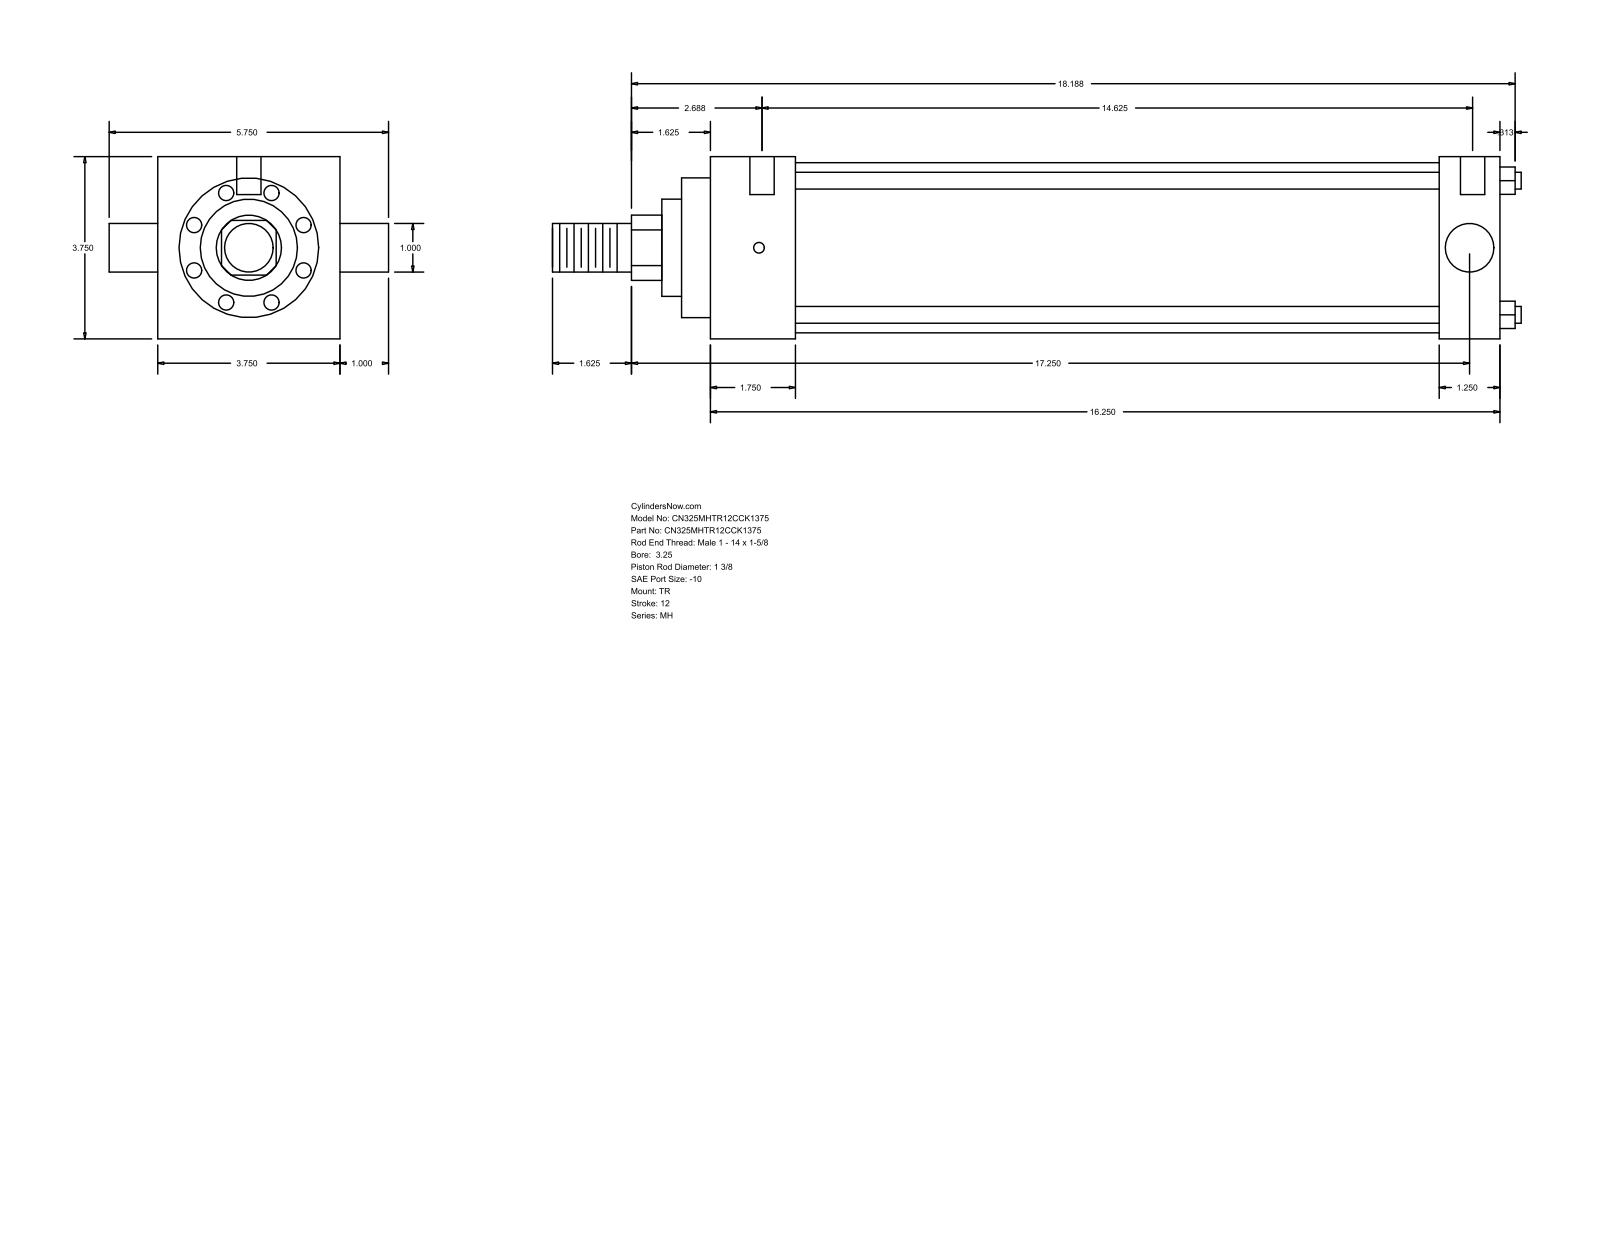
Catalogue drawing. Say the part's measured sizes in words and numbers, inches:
The part is named "MH_TR__0325_1.375". Its 3-D file was written by "GSSL Pune (CONFIG_CONTROL_DESIGN)". It is 0 solids with 86 faces: 61 planar, 25 cylindrical and 0 other. Overall it measures 19.937 by 5.75 by 3.75 inches. Round holes: 3 of diameter 0.219, 2 of diameter 0.5. Round bosses or shafts: 4 of diameter 0.345, 2 of diameter 1, 1 of diameter 3.5, 1 of diameter 2.875, 1 of diameter 2, 1 of diameter 1.375. Partial cylindrical surfaces (rounded edges, fillets, slot ends): 1 of radius 0.672. The main face-to-face distances are 3.75, 16.25, 1.75, 15, 13.25, 14.5, 1.25, 0.594, 2.344, 15.594. The hole center spacings are 0.063, 0.187, 14.625, 14.688, 14.813, 14.875.
